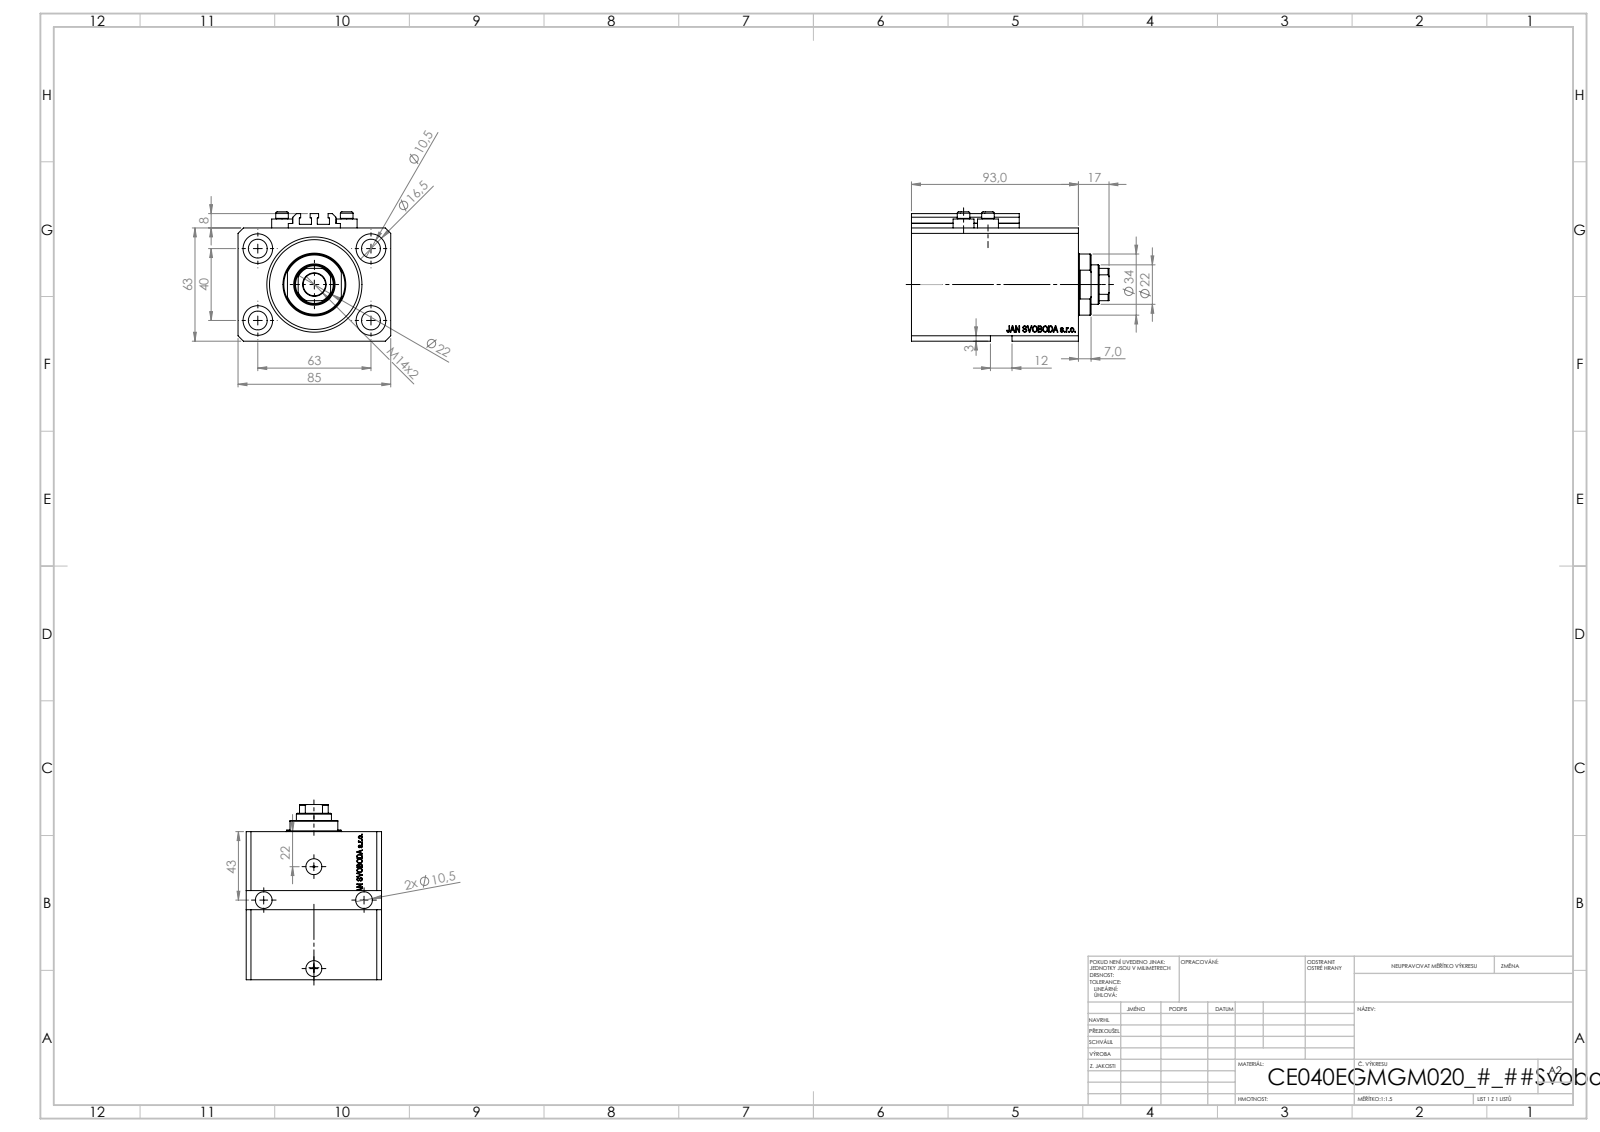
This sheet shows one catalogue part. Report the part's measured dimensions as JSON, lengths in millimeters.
{"part_name": "V250CE_VC_E; V250CE_C_VCP; ALLEN BOLT V250CE; V250CE_E_Body", "step_written_by": "SolidWorks 2019 (CONFIG_CONTROL_DESIGN)", "units": "millimeters", "bodies": {"solids": 8, "faces": 1087, "planar": 535, "cylindrical": 126, "other": 426}, "overall_size": [110, 85, 72], "volume_mm3": 437253, "surface_area_mm2": 95786, "round_holes": [[10.5, 6], [1.25, 4], [4, 4], [16.5, 4], [10, 2], [13.16, 2], [20, 2], [12.5, 1], [22, 1], [40, 1], [53, 1]], "round_bosses_or_shafts": [[11.6, 4], [7, 4], [34, 1]], "partial_cylinders_radius": [[0.2, 10], [10.5, 1]], "face_to_face_distances": [63, 85, 93, 17, 76, 11.4, 64.6, 81.6, 3, 65], "hole_center_spacings": [37.31, 63, 13.6, 15.4, 24.96, 28.02, 28.43, 33.62]}
